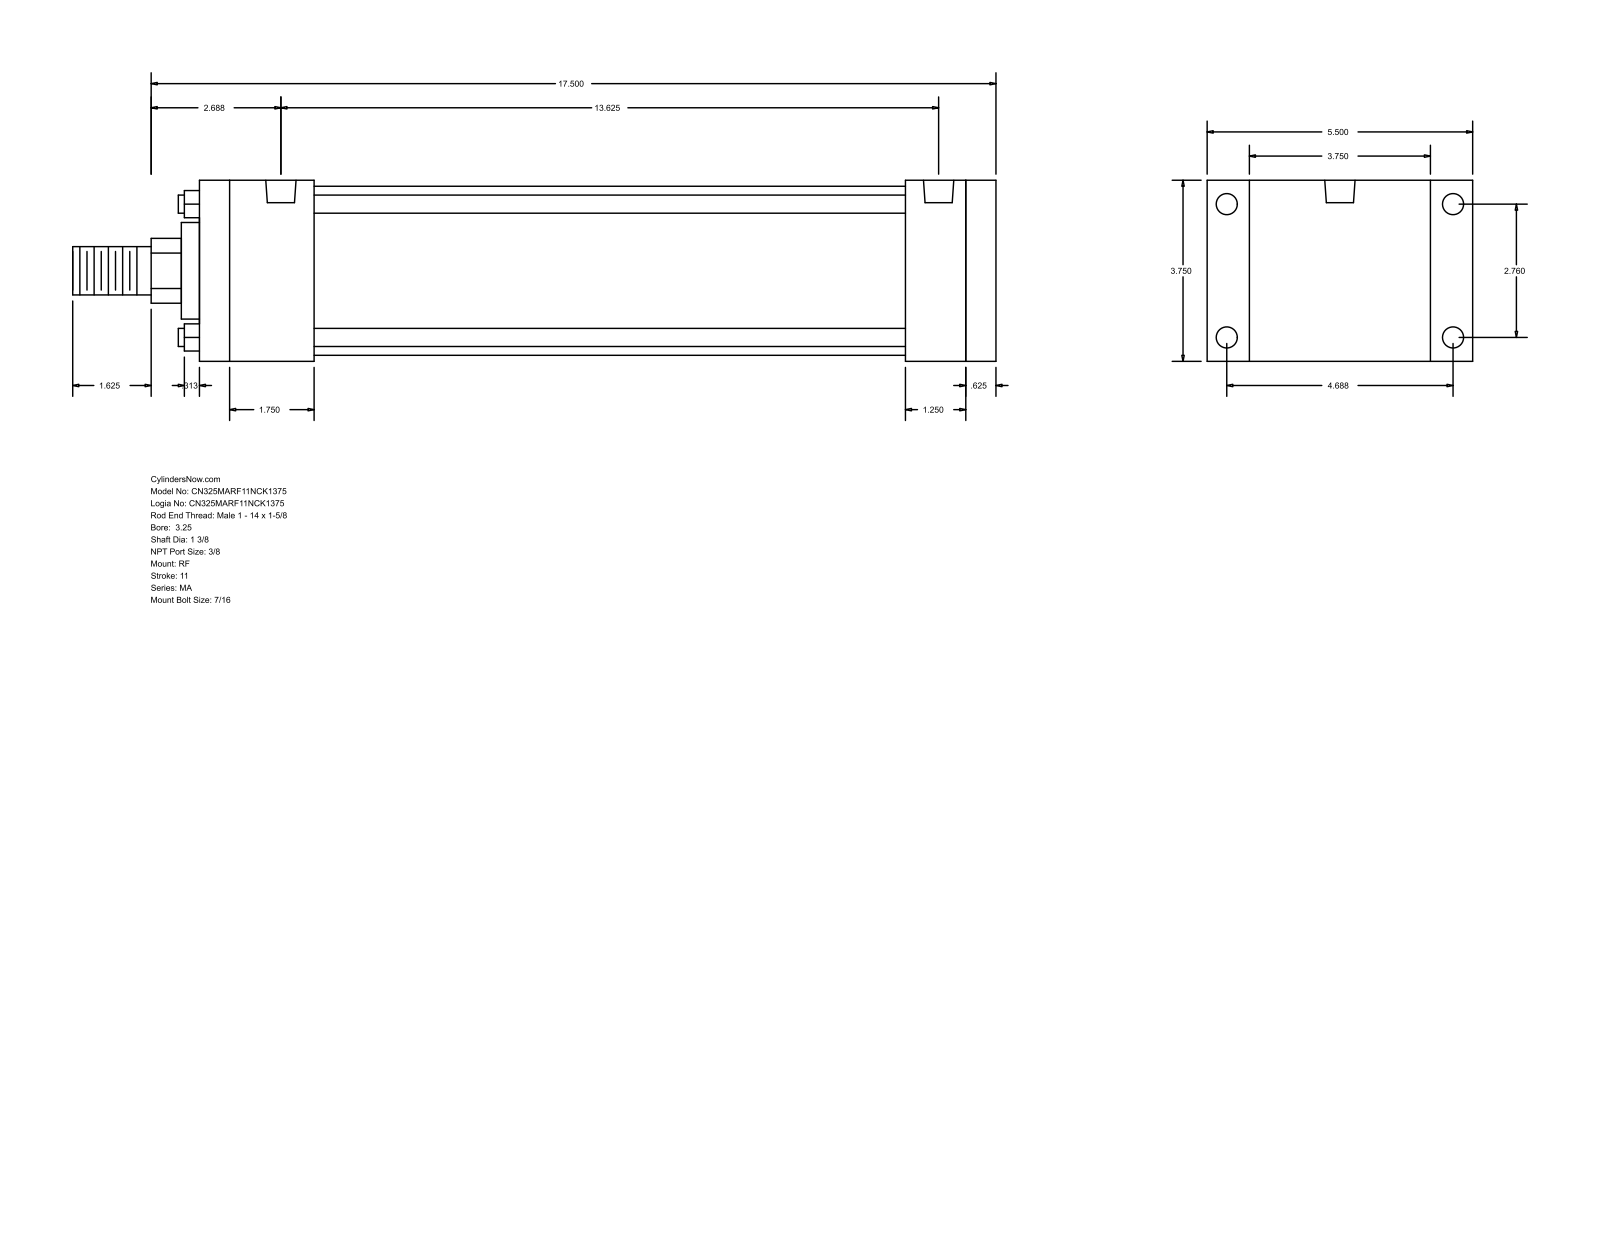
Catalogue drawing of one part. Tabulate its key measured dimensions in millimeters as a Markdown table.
| quantity | value |
| --- | --- |
| part name | MA_RF__0325_1.375 |
| STEP written by | GSSL Pune (CONFIG_CONTROL_DESIGN) |
| units | millimeters |
| bodies | 0 solids, 92 faces (64 planar, 28 cylindrical, 0 other) |
| overall size | 485.77 × 139.7 × 95.25 |
| round holes (diameter × count) | 11.11 × 8, 15.93 × 2 |
| round bosses / shafts (diameter × count) | 9.53 × 4, 88.9 × 1, 50.8 × 1, 34.92 × 1, 25.4 × 1 |
| partial cylindrical surfaces (radius × count) | 17.06 × 1 |
| main face-to-face distances | 95.24, 419.1, 15.88, 403.22, 22.23, 117.47, 371.48, 31.74, 47.62, 60.32 |
| hole center spacings | 4.77, 70.1, 119.06, 138.16, 336.54, 341.31, 346.08 |
